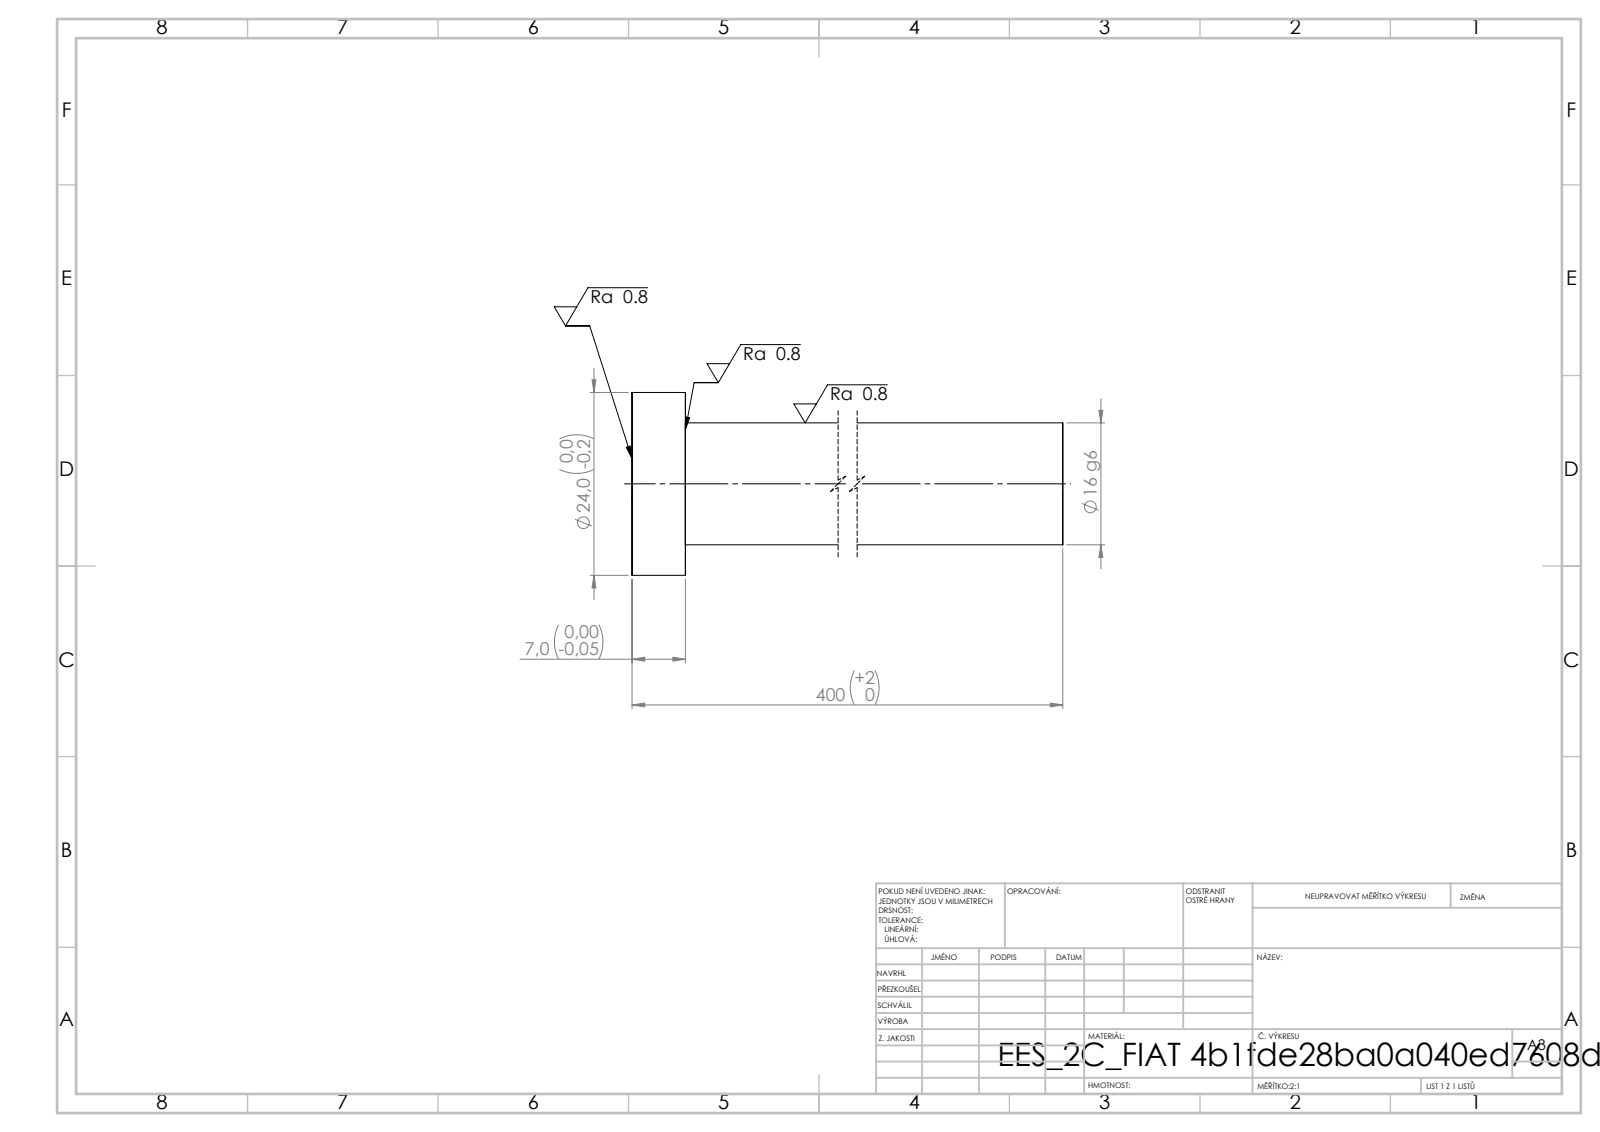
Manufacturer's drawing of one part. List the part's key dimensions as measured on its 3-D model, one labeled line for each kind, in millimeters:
STEP written by: SolidWorks 2019 (CONFIG_CONTROL_DESIGN)
Units: millimetres
Bodies: 1 solid, 7 faces (3 planar, 4 cylindrical, 0 other)
Overall size (bounding box): 400 × 24 × 24
Volume: 82 184 mm³ · Surface area: 21 187 mm²
Round bosses / shafts (diameter × count): ⌀24 ×1, ⌀16 ×1
Main face-to-face distances: 7, 400, 393
